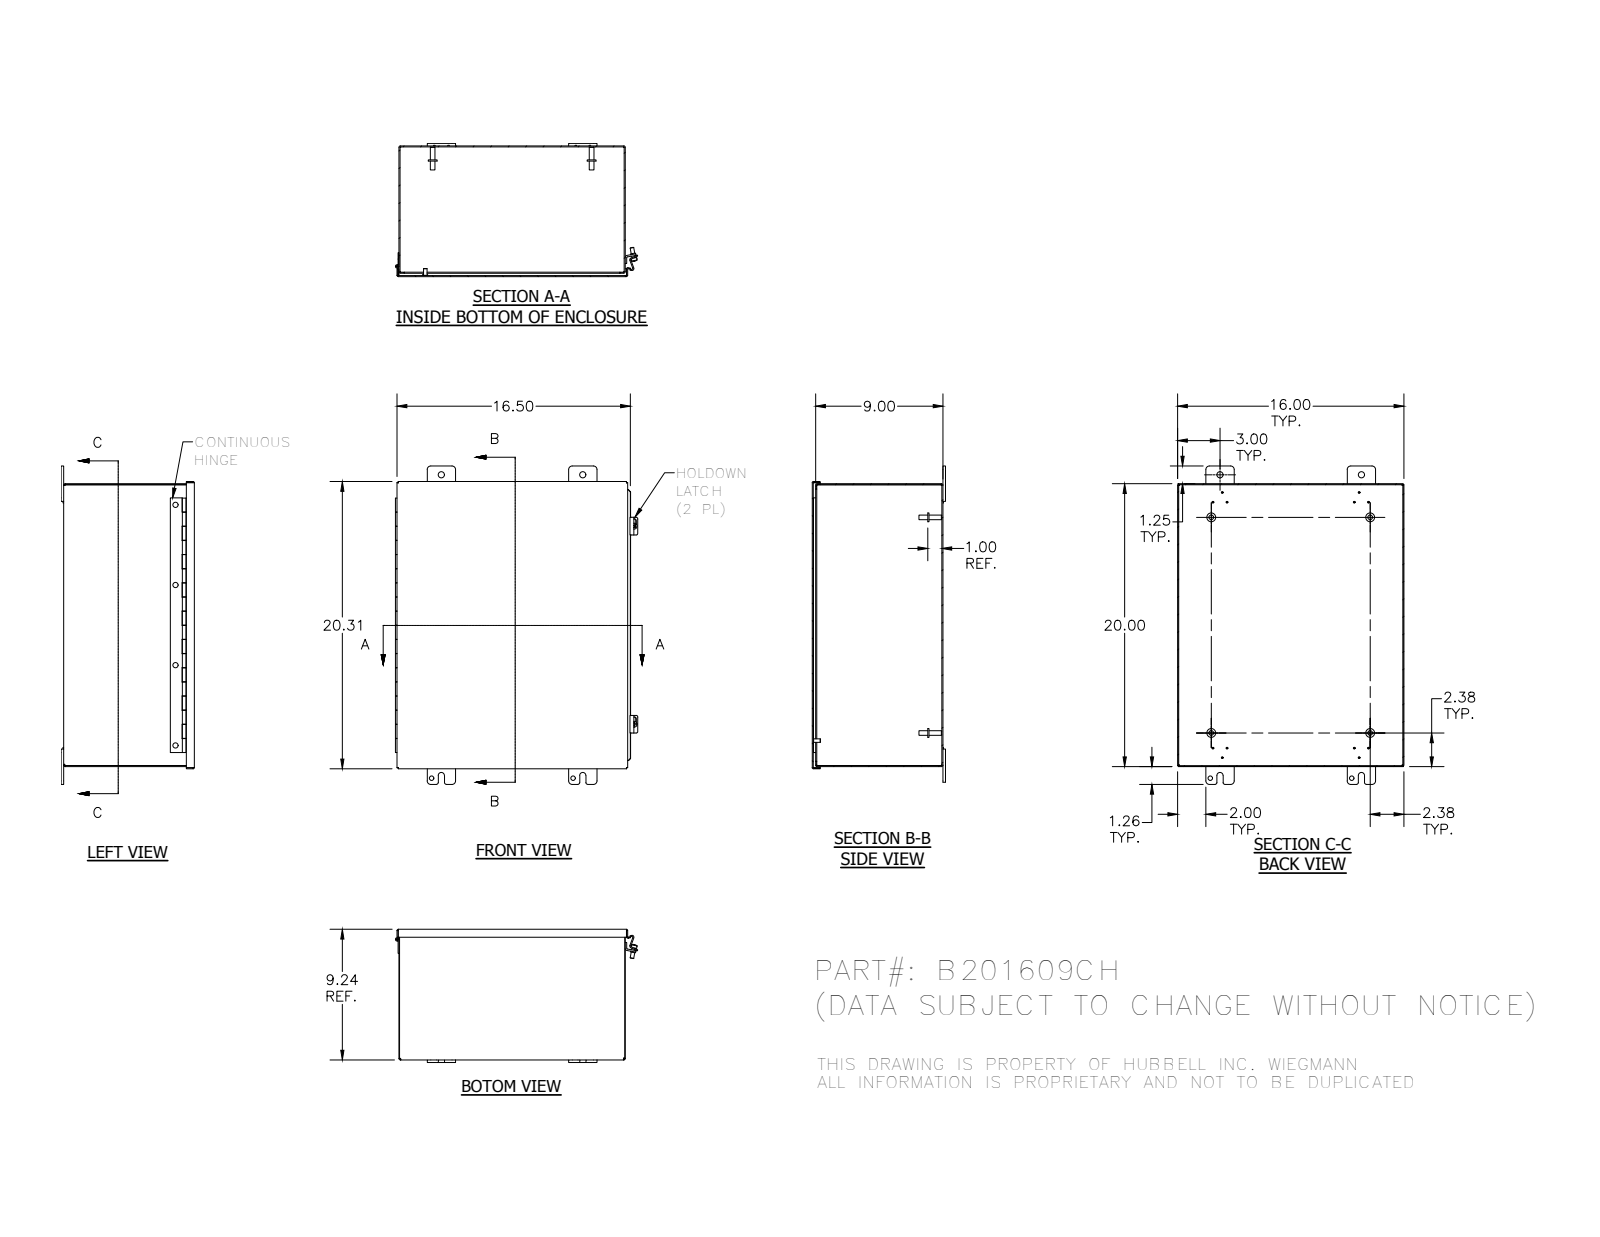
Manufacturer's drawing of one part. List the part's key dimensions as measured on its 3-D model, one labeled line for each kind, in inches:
Part name (STEP PRODUCT): B201609CH; B201609CHBKP; B2016CHLID; H6010100 (+8 more)
STEP written by: Autodesk Inventor 2012 (AUTOMOTIVE_DESIGN)
Units: inches
Bodies: 20 solids, 617 faces (371 planar, 177 cylindrical, 69 other)
Overall size (bounding box): 22.505 × 17.136 × 9.423
Volume: 106.4 in³ · Surface area: 2 860 in²
Round holes (diameter × count): ⌀0.11 ×4, ⌀0.313 ×4, ⌀0.375 ×4, ⌀0.438 ×4, ⌀0.196 ×2, ⌀0.125 ×1, ⌀0.125 ×1
Round bosses / shafts (diameter × count): ⌀0.625 ×4, ⌀0.33 ×4, ⌀0.25 ×4, ⌀0.41 ×2, ⌀0.344 ×2, ⌀0.337 ×1, ⌀0.12 ×1
Partial cylindrical surfaces — rounded edges, fillets, slot ends (radius × count): R0.125 ×16, R0.25 ×16, R0.031 ×8, R0.063 ×8, R0.07 ×8, R0.105 ×8, R0.016 ×5, R0.09 ×5
Main face-to-face distances: 0.074, 9.169, 15.926, 9.243, 9.095, 19.926, 16, 15.852, 19.852, 20
Hole centre spacings: 10, 1.593, 20.005, 22.365, 0.75, 5.667, 9.423, 10.783
